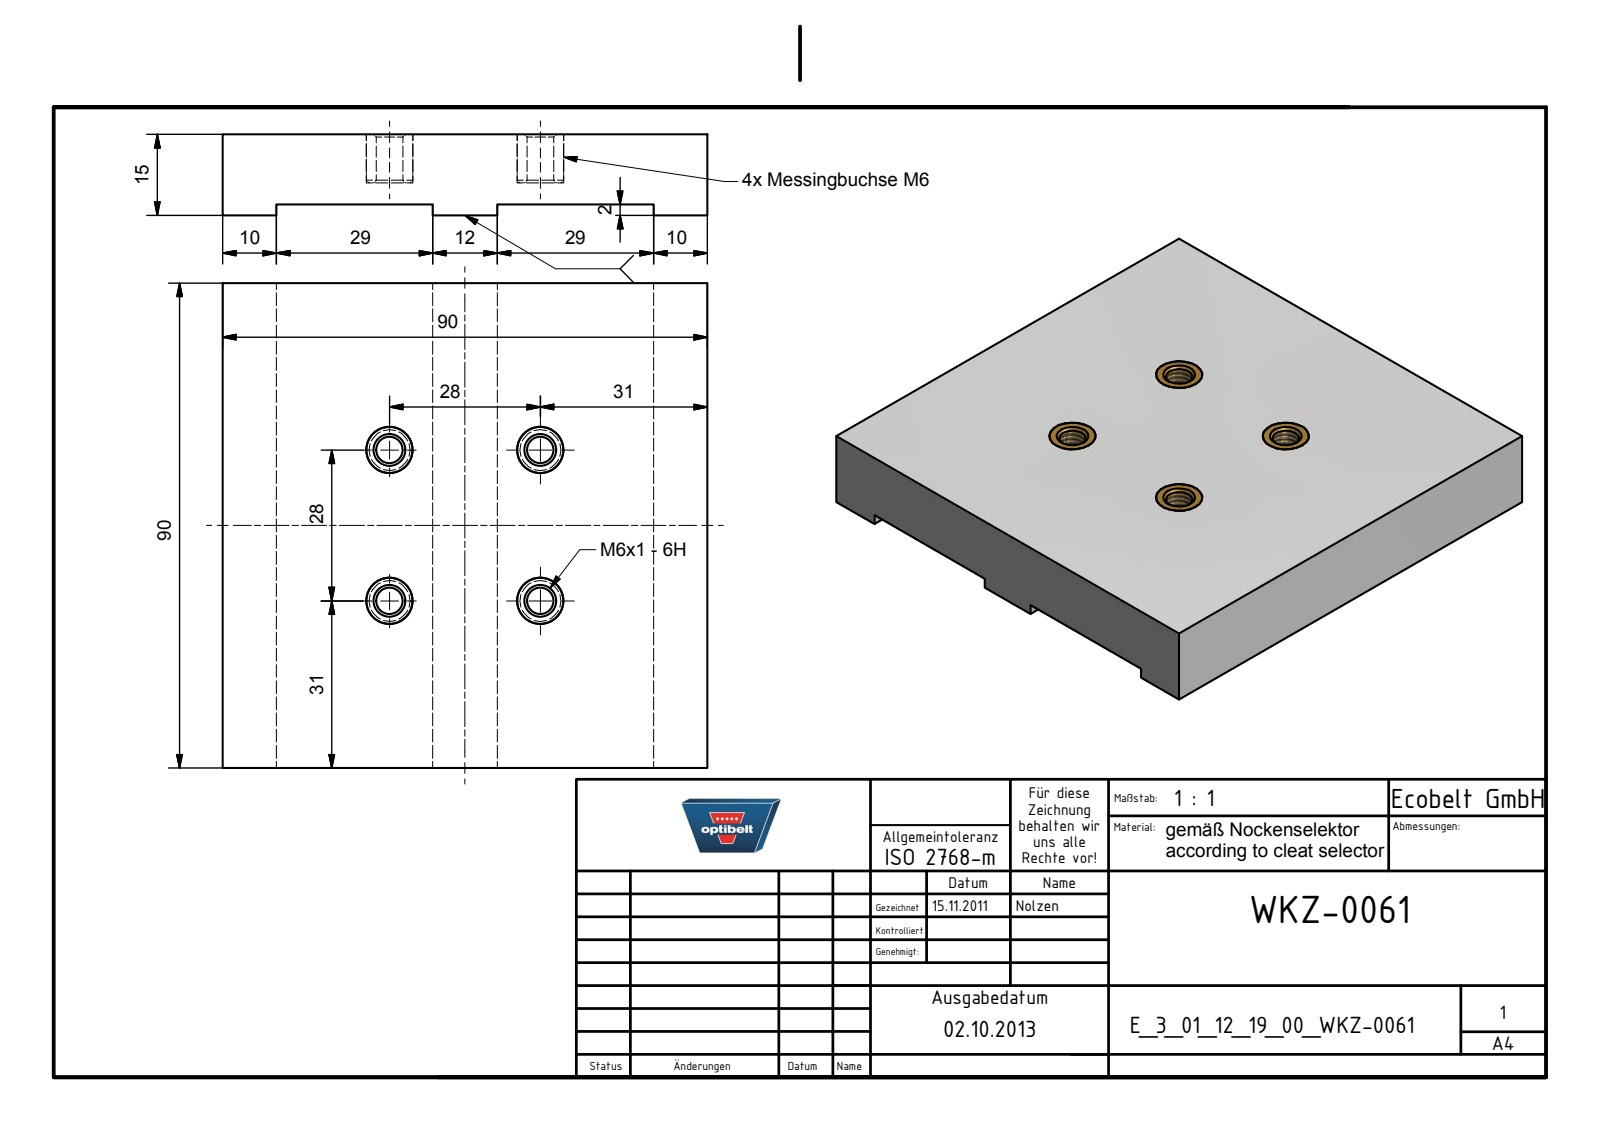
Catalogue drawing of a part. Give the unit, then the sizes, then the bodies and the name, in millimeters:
Units: millimetres
Overall size (bounding box): 90 × 90 × 15
Round holes (diameter × count): ⌀4.92 ×4, ⌀8.6 ×4
Main face-to-face distances: 13, 15, 2, 90, 10, 39, 51, 80, 29, 41
Hole centre spacings: 28, 39.6
Volume: 110 347 mm³ · Surface area: 24 836 mm²
Bodies: 5 solids, 50 faces (26 planar, 12 cylindrical, 12 other)
Part name (STEP PRODUCT): E_3_01_12_19_00_WKZ-0061; E_3_01_12_19_00_WKZ-0061_Teil1; E_3_01_12_19_00_WKZ-0061_Teil2
STEP written by: Autodesk Inventor 2025 (AUTOMOTIVE_DESIGN)
